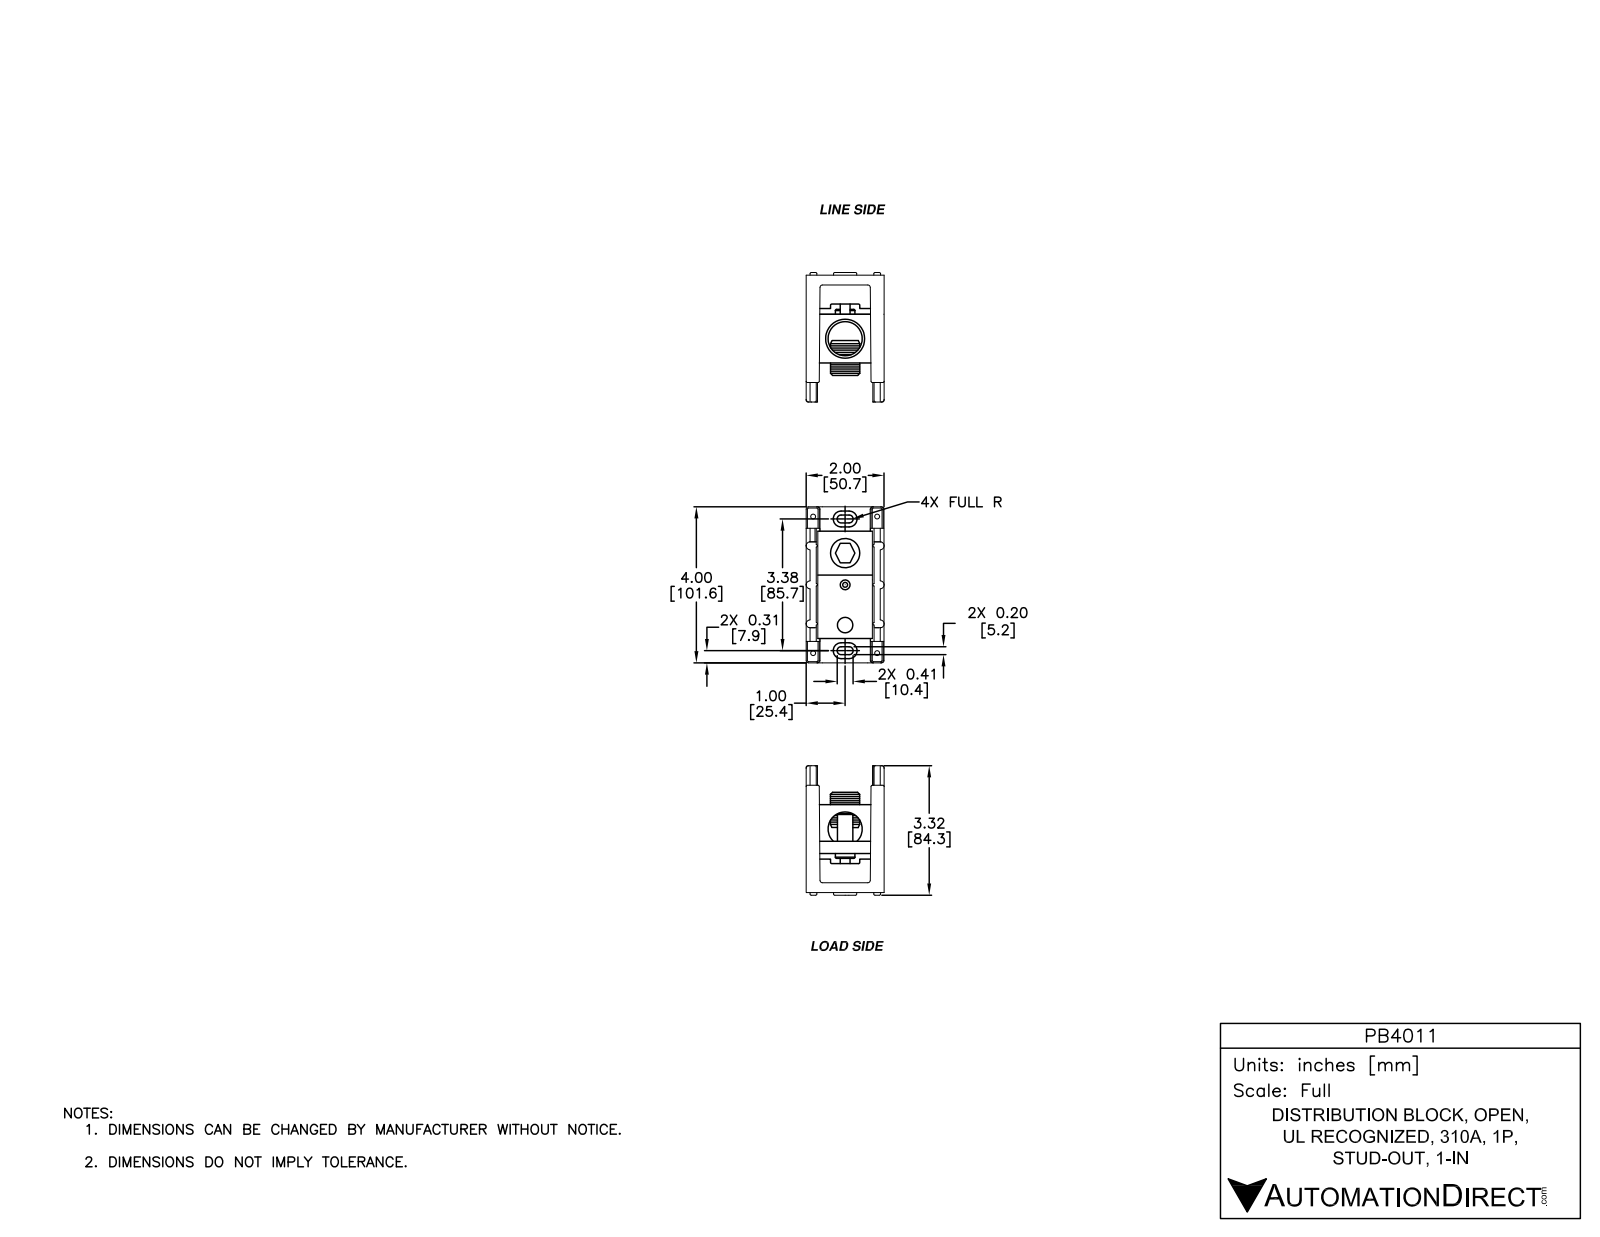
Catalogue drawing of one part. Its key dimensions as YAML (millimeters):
part_name: "PB4011"
step_written_by: "SolidWorks 2014 (AUTOMOTIVE_DESIGN)"
units: millimeters
bodies: {solids: 6, faces: 454, planar: 144, cylindrical: 210, other: 100}
overall_size: [101.6, 85.1, 50.8]
volume: 155700
surface_area: 69030
round_holes:
  - {diameter: 3.2, count: 4}
  - {diameter: 19.1, count: 2}
  - {diameter: 6.4, count: 1}
  - {diameter: 10, count: 1}
  - {diameter: 12.7, count: 1}
  - {diameter: 22.2, count: 1}
round_bosses_or_shafts:
  - {diameter: 4.4, count: 4}
  - {diameter: 1.6, count: 2}
  - {diameter: 12.7, count: 1}
partial_cylinders:
  - {radius: 0.8, count: 50}
  - {radius: 2.5, count: 22}
  - {radius: 1.6, count: 18}
  - {radius: 1.6, count: 12}
  - {radius: 5.2, count: 8}
  - {radius: 2.4, count: 4}
face_to_face_distances: [41.7, 2.5, 6.6, 4, 44.2, 48.3, 50.8, 37.6, 45.7, 9.1]
hole_center_spacings: [49.1, 27.7, 31.6, 41.7, 68.4, 73.7, 88.9, 98.2]
